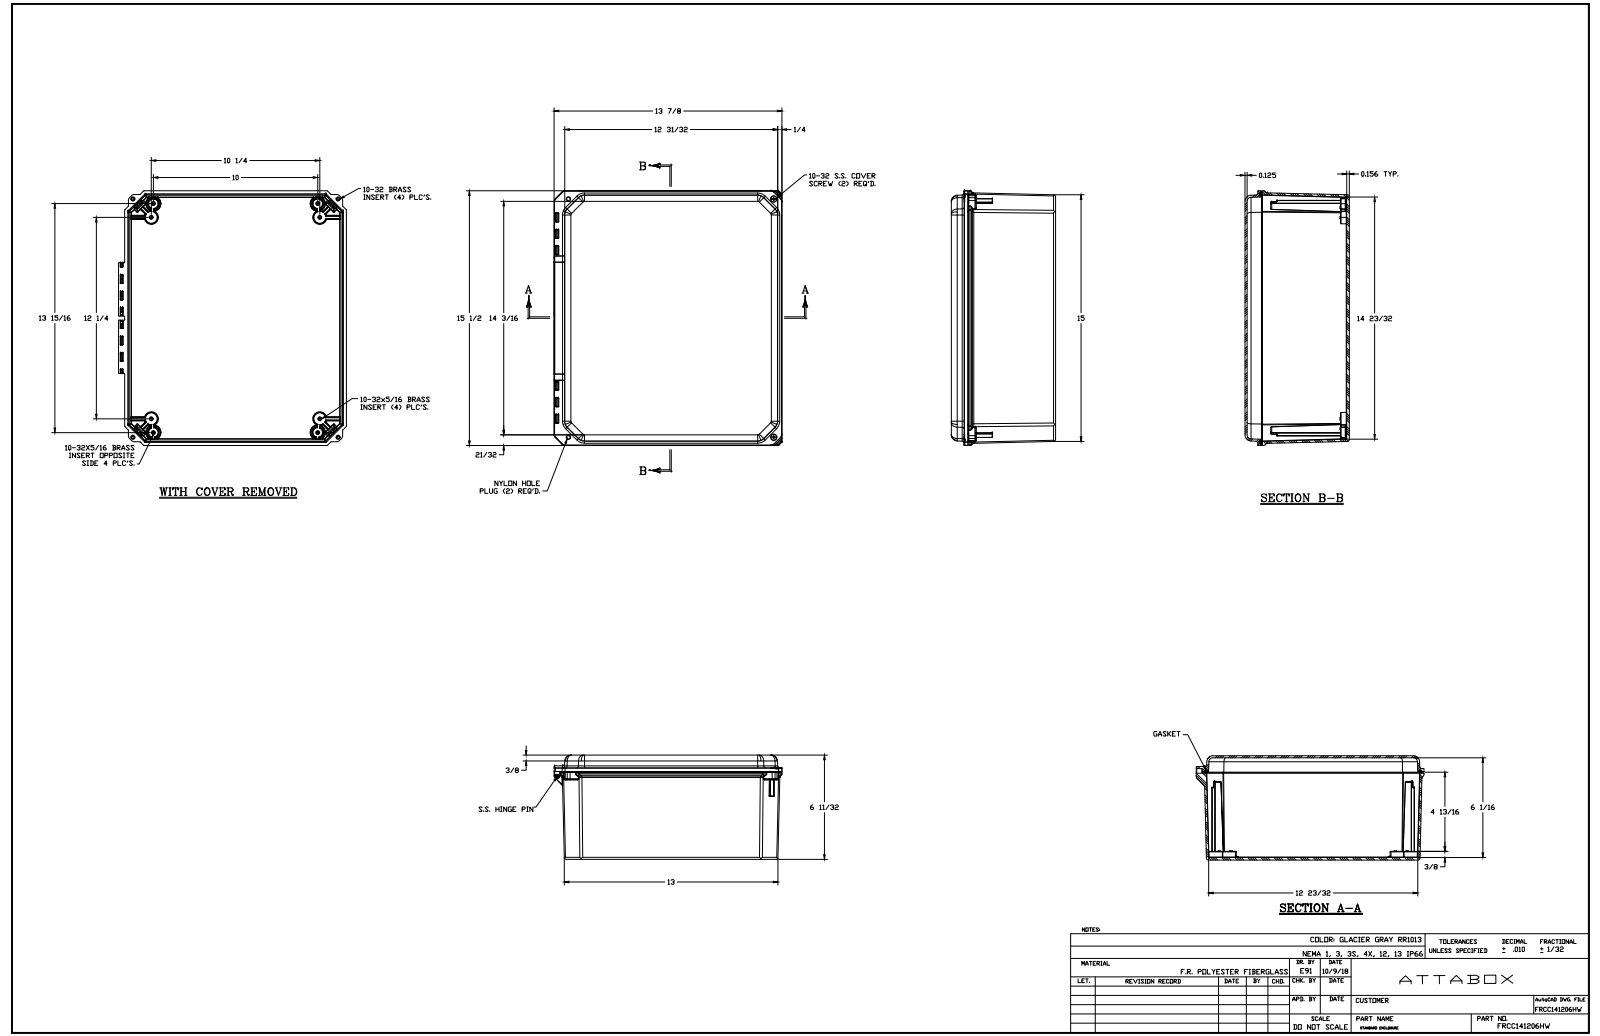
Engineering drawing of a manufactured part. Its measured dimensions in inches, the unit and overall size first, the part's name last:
Units: inches
Overall size (bounding box): 15.49 × 13.866 × 6.394
Round holes (diameter × count): ⌀0.156 ×12, ⌀0.152 ×8, ⌀0.219 ×4, ⌀0.252 ×4, ⌀0.312 ×4, ⌀0.15 ×2, ⌀0.137 ×1
Round bosses / shafts (diameter × count): ⌀0.246 ×12, ⌀0.87 ×4, ⌀0.45 ×2, ⌀0.209 ×2, ⌀0.199 ×2, ⌀0.135 ×1
Partial cylindrical surfaces — rounded edges, fillets, slot ends (radius × count): R0.01 ×205, R0.005 ×116, R0.02 ×59, R0.03 ×38, R0.125 ×29, R0.03 ×24, R0.09 ×24, R0.25 ×24
Main face-to-face distances: 0.125, 0.156, 6.218, 6.062, 6.343, 6.187, 0.14, 0.139, 0.937, 5.281
Hole centre spacings: 1.582, 10.16, 0.841, 1.277, 10.252, 11.248, 11.425, 13.081
Volume: 110.3 in³ · Surface area: 1 572 in²
Bodies: 23 solids, 2113 faces (586 planar, 804 cylindrical, 723 other)
Part name (STEP PRODUCT): FRCC141206HW
STEP written by: SolidWorks 2018 (AUTOMOTIVE_DESIGN)
